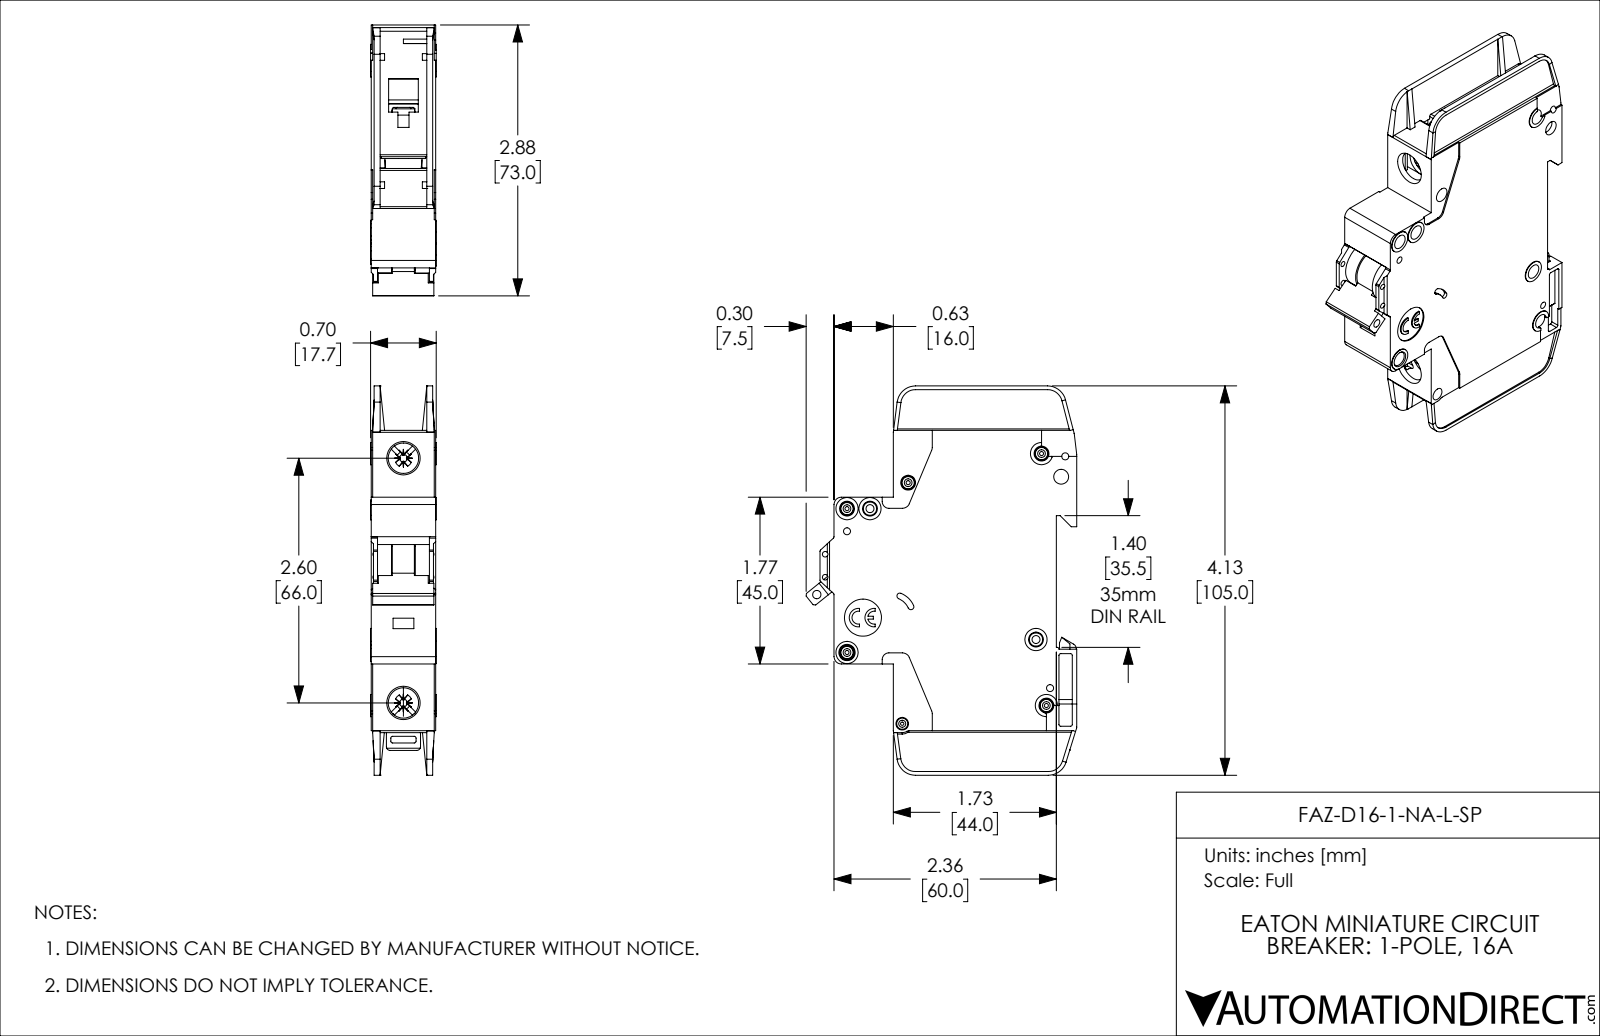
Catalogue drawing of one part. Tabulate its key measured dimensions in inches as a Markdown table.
| quantity | value |
| --- | --- |
| part name | FAZ-D16-1-NA-L-SP |
| STEP written by | SolidWorks 2019 (AUTOMOTIVE_DESIGN) |
| units | inches |
| bodies | 1 solid, 1127 faces (671 planar, 357 cylindrical, 99 other) |
| overall size | 4.134 × 2.876 × 0.697 |
| volume | 4.682 in³ |
| surface area | 41.01 in² |
| round holes (diameter × count) | 0.157 × 8, 0.043 × 5, 0.075 × 4, 0.059 × 2, 0.085 × 2, 0.323 × 2, 0.035 × 1, 0.089 × 1, 0.098 × 1, 0.134 × 1, 0.394 × 1 |
| round bosses / shafts (diameter × count) | 0.13 × 5, 0.236 × 4, 0.118 × 2, 0.098 × 1 |
| partial cylindrical surfaces (radius × count) | 0.02 × 42, 0.016 × 10, 0.039 × 10, 0.079 × 8, 0.197 × 5, 0.008 × 4, 0.026 × 4, 0.043 × 4 |
| main face-to-face distances | 0.047, 0.685, 0.591, 0.638, 0.094, 0.543, 0.016, 0.031, 0.496, 0.575 |
| hole center spacings | 0.244, 0.537, 0.87, 0.189, 0.199, 0.204, 0.221, 0.24 |
